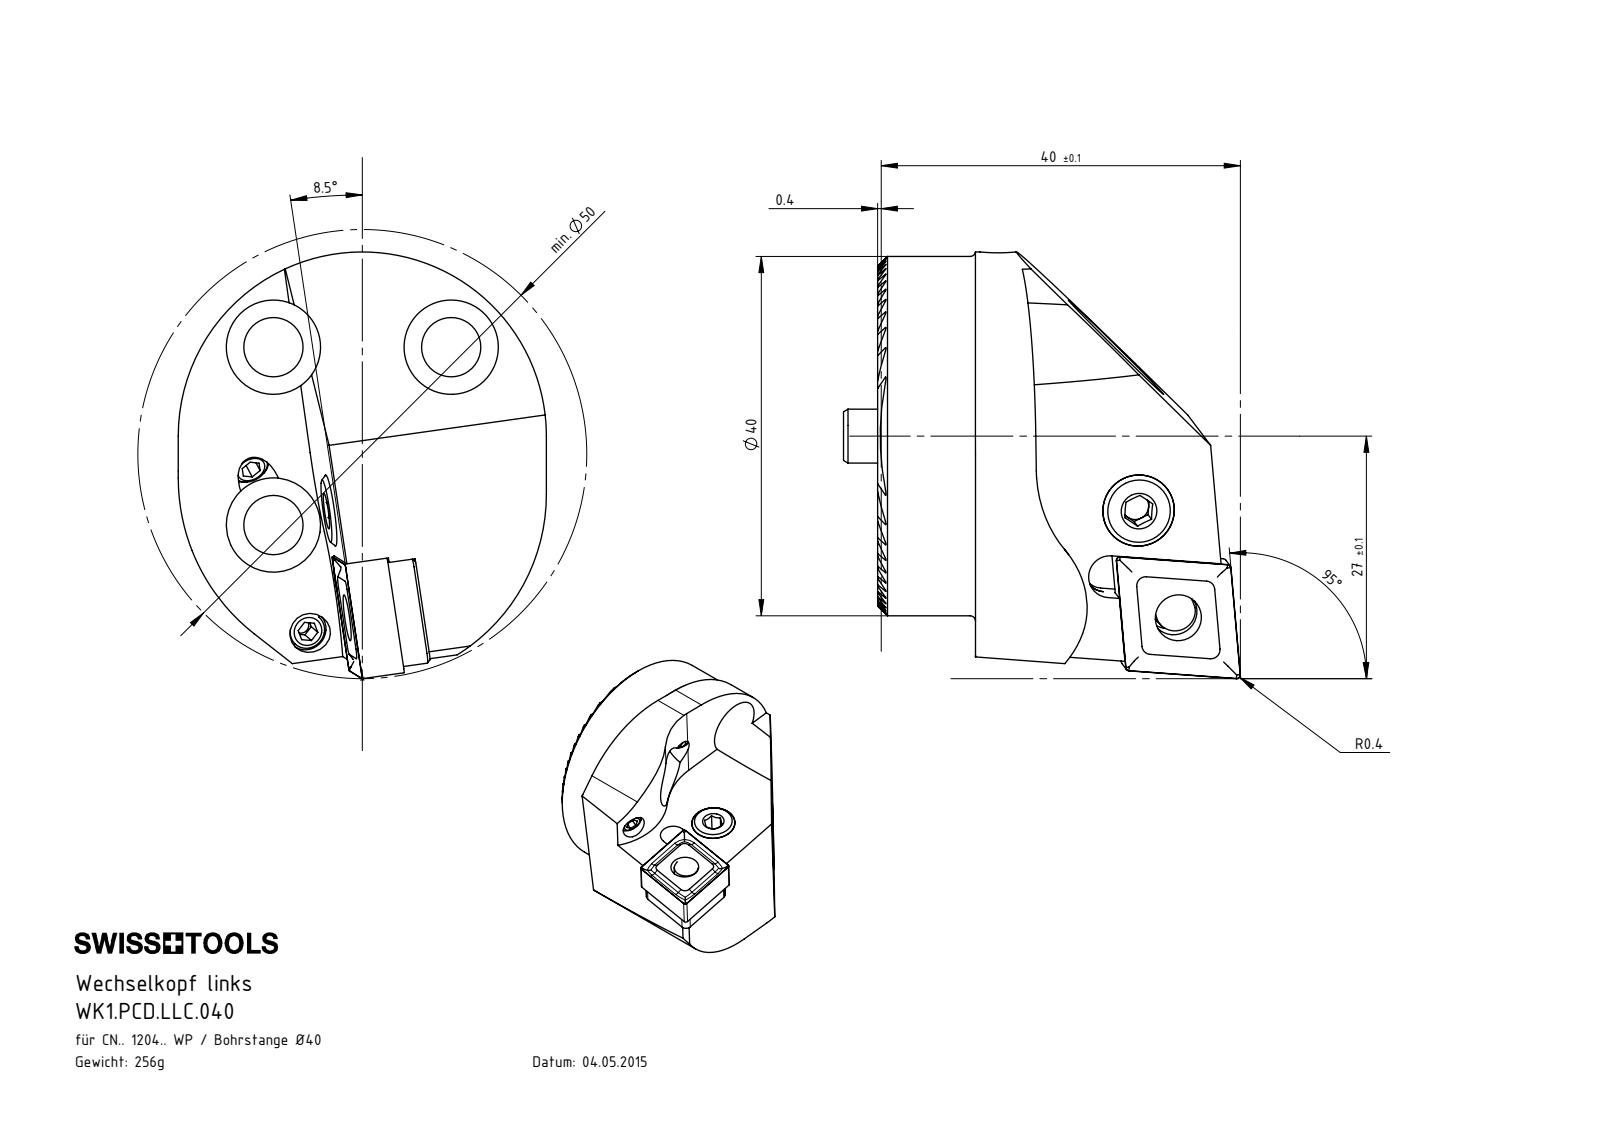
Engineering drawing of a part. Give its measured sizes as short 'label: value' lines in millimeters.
name: WCD-ER4.101.017_A; WK2-ER1.001.012_A_Fertigbearbeitung; WK1-PCD.LLC.040_A; WK1.PCD.LLC.040 (+6 more)
written by: SolidWorks 2017 (AUTOMOTIVE_DESIGN)
unit: mm
bodies: 15 solids, 671 faces (262 planar, 224 cylindrical, 185 other)
size: 47.5 × 44.2 × 41
volume: 31 788 mm³; area: 14 483 mm²
holes: 5× ⌀3.3, 3× ⌀3, 3× ⌀6.6, 3× ⌀10.5, 2× ⌀1.7, 2× ⌀4, 2× ⌀4.5, 1× ⌀4.2, 1× ⌀5.16, 1× ⌀6.4, 1× ⌀7, 1× ⌀8.4
bosses: 5× ⌀4, 1× ⌀40, 1× ⌀8, 1× ⌀7.9, 1× ⌀6.4, 1× ⌀6, 1× ⌀4.5, 1× ⌀3.55
rounds: 26× R0.12, 4× R0.4, 4× R1, 2× R2.5, 1× R2.1, 1× R2.2, 1× R2.35, 1× R2.8
face distances: 1.3, 2.6, 3.9, 12.99, 5.2, 11.69, 9.09, 10.39, 7.79, 6.5
hole spacings: 14, 19.8, 12.81, 12.86, 28
